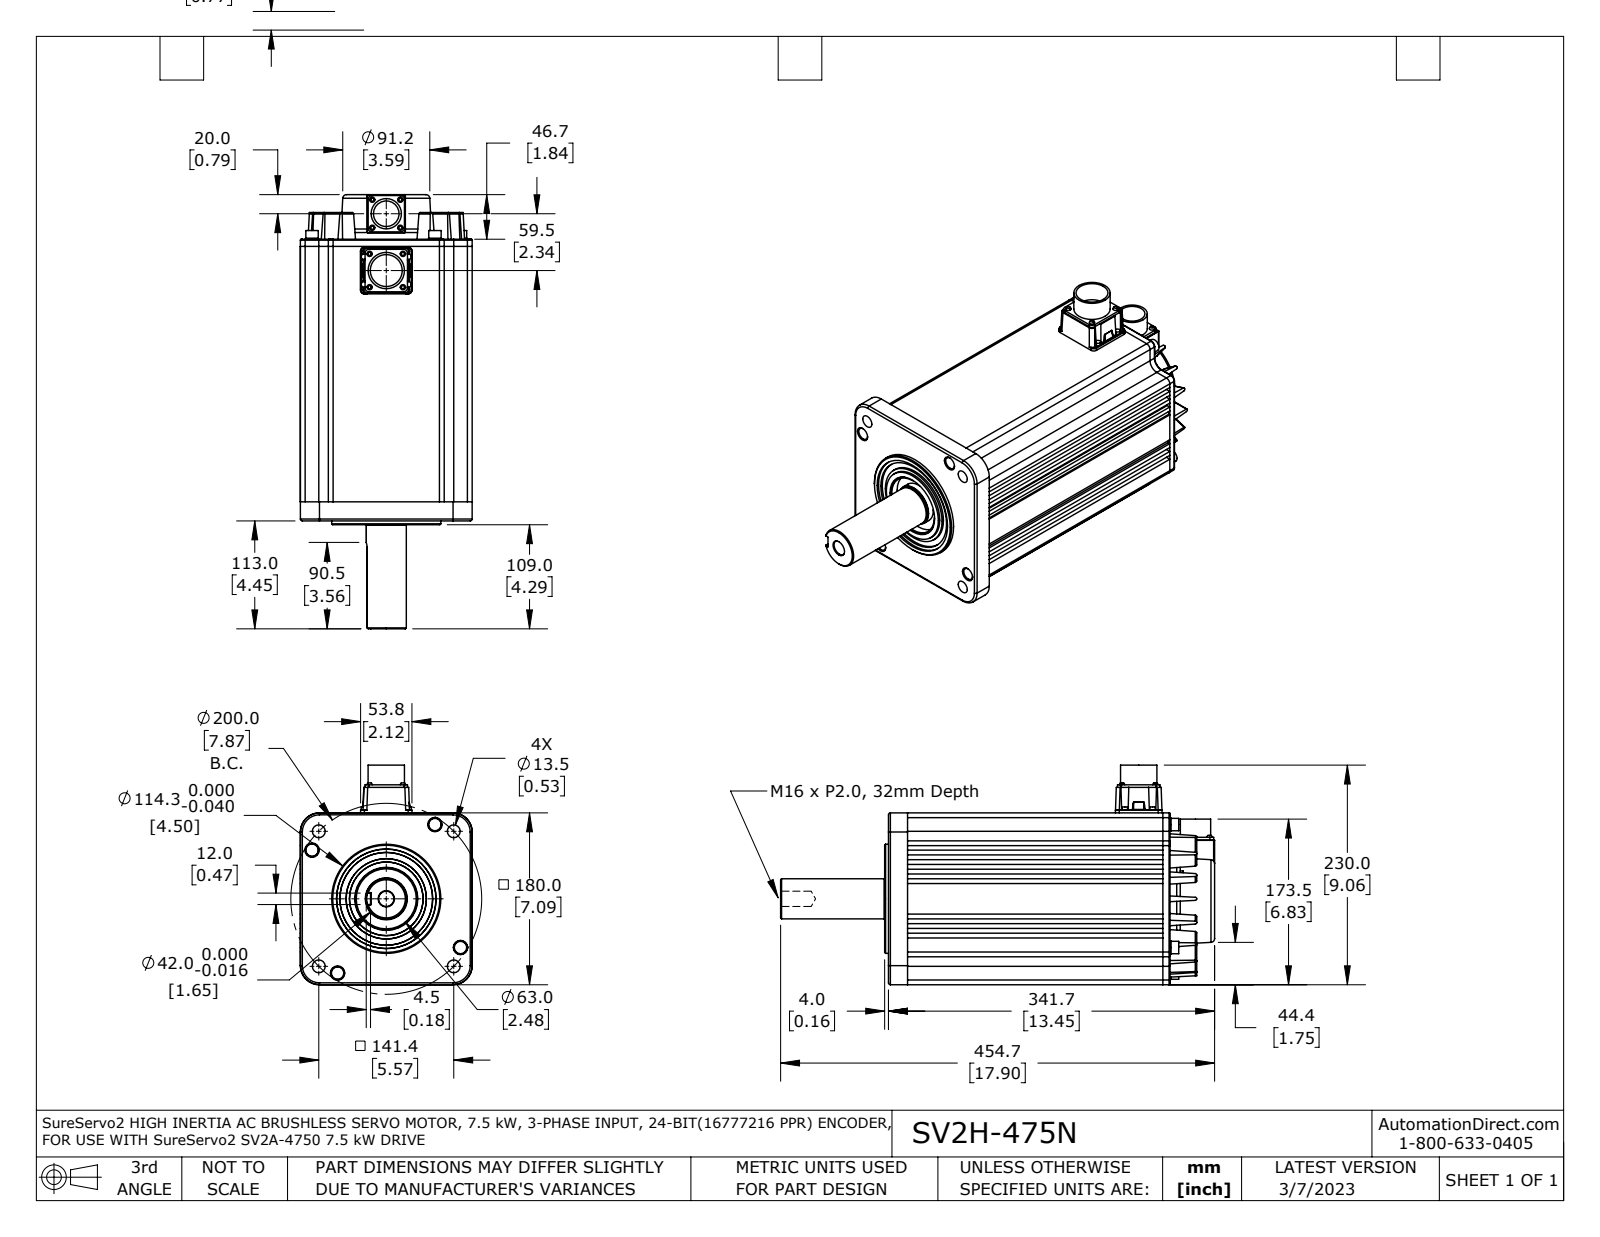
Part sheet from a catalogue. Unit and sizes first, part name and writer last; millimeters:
Units: millimetres
Overall size (bounding box): 454.7 × 230 × 180
Round holes (diameter × count): ⌀13.5 ×4, ⌀16 ×1, ⌀26.9 ×1, ⌀33.5 ×1, ⌀63 ×1
Round bosses / shafts (diameter × count): ⌀5.5 ×7, ⌀13.4 ×4, ⌀13 ×4, ⌀8 ×4, ⌀116 ×1, ⌀114.3 ×1, ⌀44 ×1, ⌀42.5 ×1
Partial cylindrical surfaces — rounded edges, fillets, slot ends (radius × count): R0.5 ×22, R1.6 ×16, R4 ×16, R5 ×16, R1 ×12, R2 ×4, R10 ×4, R20 ×4
Main face-to-face distances: 5, 10, 180, 29.3, 15, 150.7, 77, 82, 72, 20
Hole centre spacings: 100, 141.4, 200, 59.5
Volume: 9 090 000 mm³ · Surface area: 425 000 mm²
Bodies: 1 solid, 622 faces (309 planar, 209 cylindrical, 104 other)
Part name (STEP PRODUCT): SV2H-475N
STEP written by: SolidWorks 2021 (AUTOMOTIVE_DESIGN)
